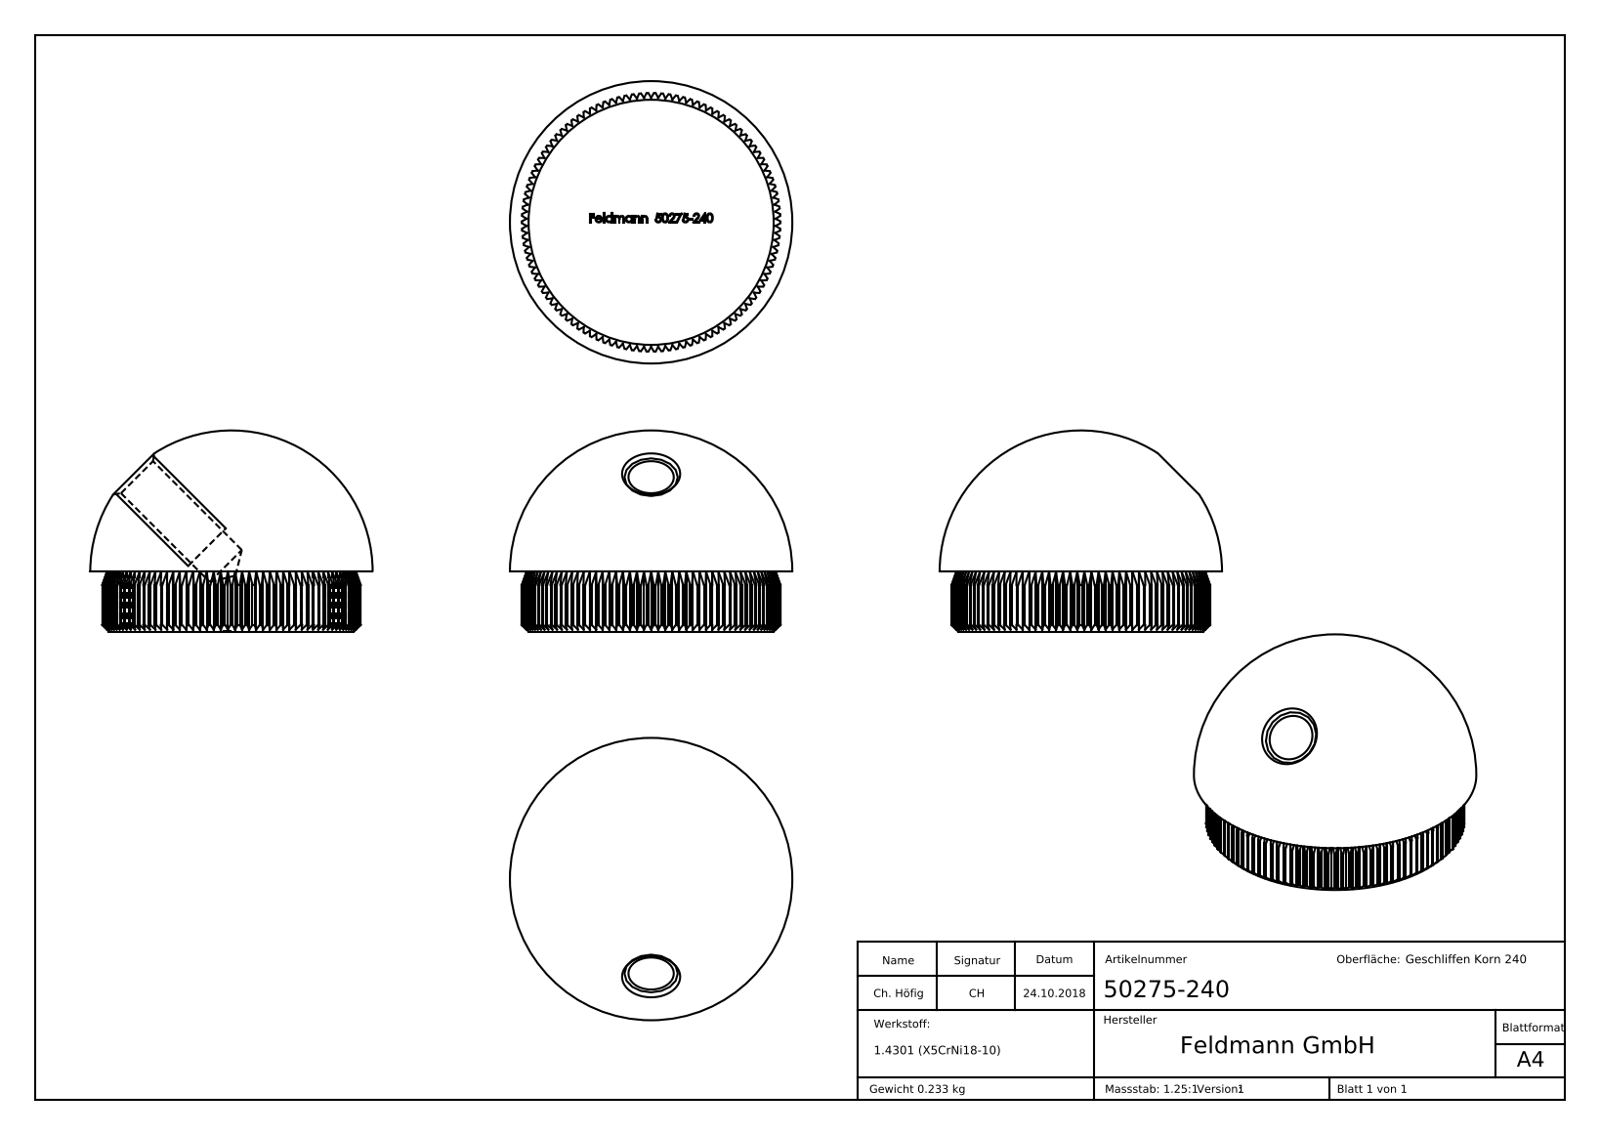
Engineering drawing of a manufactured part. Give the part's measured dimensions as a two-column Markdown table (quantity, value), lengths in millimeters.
| quantity | value |
| --- | --- |
| part name | 50275-240 |
| STEP written by | SolidWorks 2015 (CONFIG_CONTROL_DESIGN) |
| units | millimeters |
| bodies | 1 solid, 592 faces (306 planar, 93 cylindrical, 193 other) |
| overall size | 42.4 × 42.4 × 30.2 |
| volume | 29 521 mm³ |
| surface area | 6 294 mm² |
| round holes (diameter × count) | 6.8 × 1 |
| partial cylindrical surfaces (radius × count) | 19.4 × 1 |
| main face-to-face distances | 18.7, 9, 18.72, 18.71, 18.68, 18.69, 8.9, 9.35, 1.32, 0.44 |
